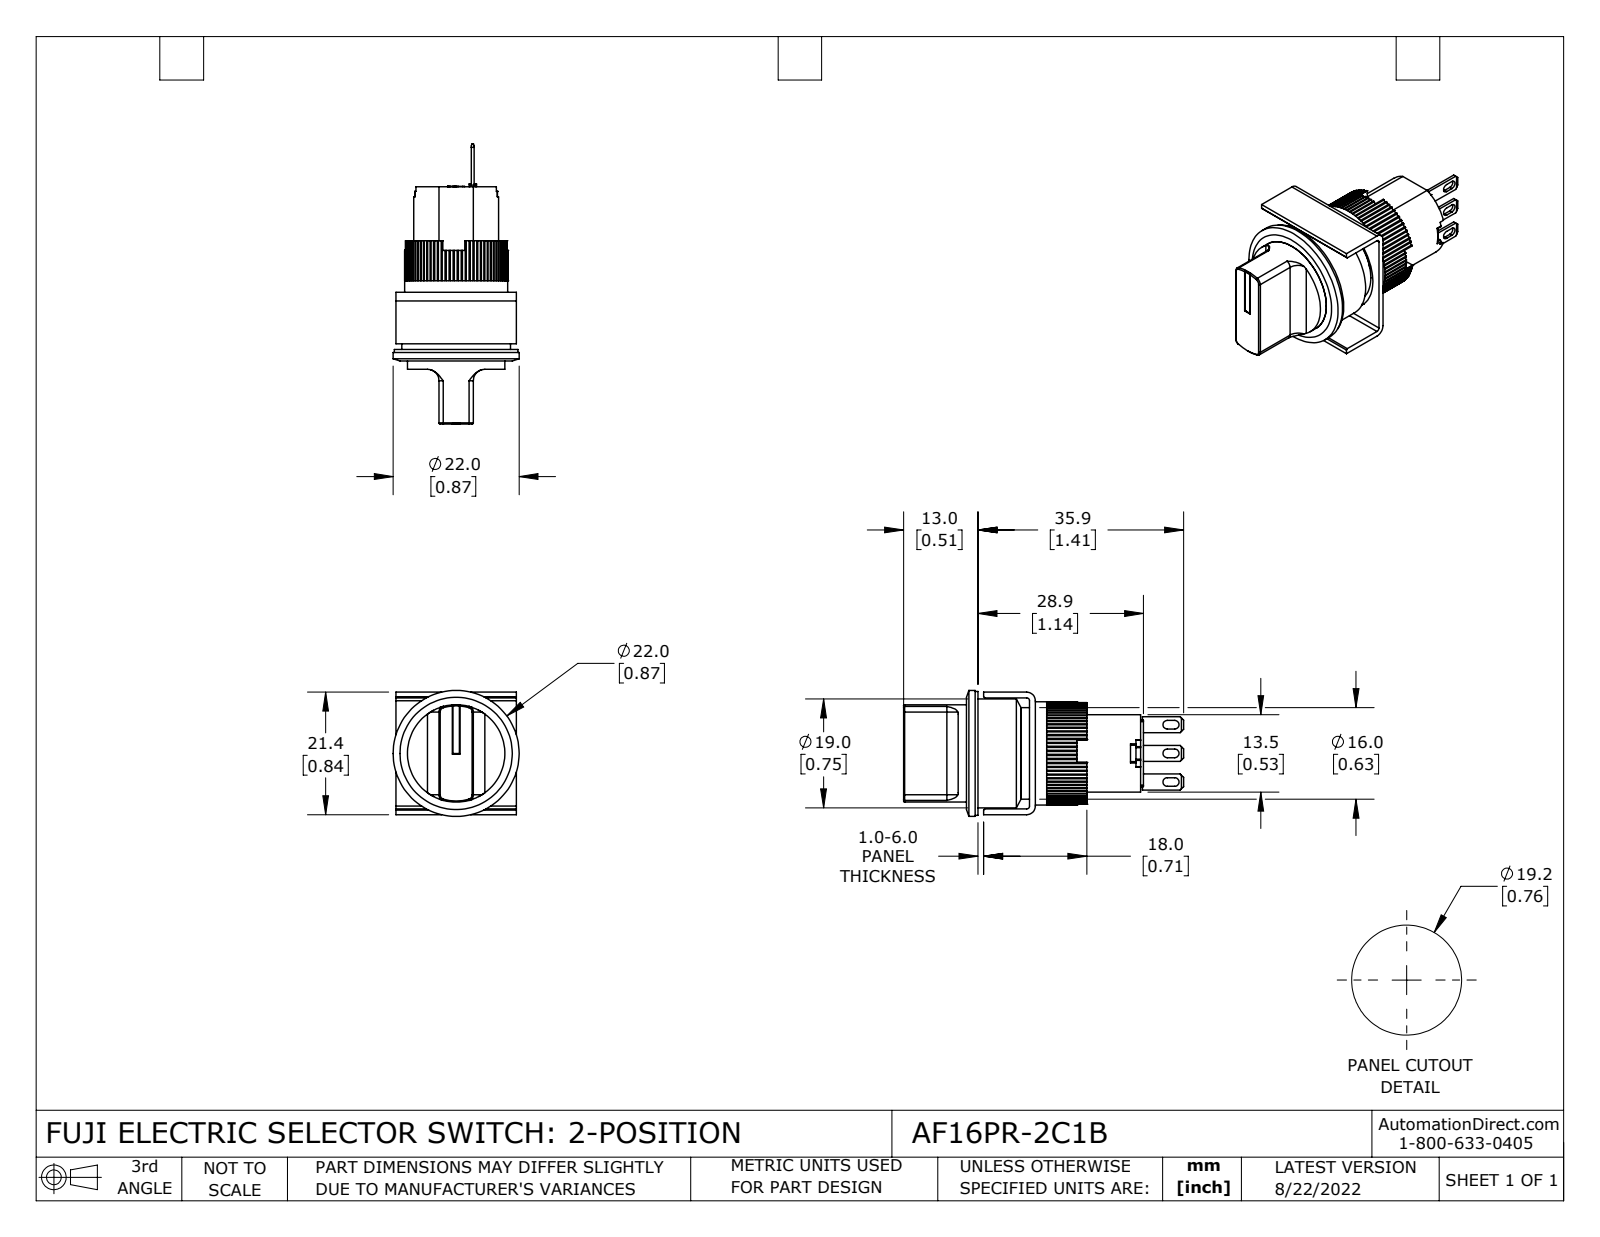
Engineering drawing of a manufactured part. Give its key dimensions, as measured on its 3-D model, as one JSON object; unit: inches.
{"part_name": "AF16PR-2C1B", "step_written_by": "SolidWorks 2021 (CONFIG_CONTROL_DESIGN)", "units": "inches", "bodies": {"solids": 9, "faces": 638, "planar": 443, "cylindrical": 180, "other": 15}, "overall_size": [1.925, 0.866, 0.866], "volume_in3": 0.491, "surface_area_in2": 10.18, "round_holes": [[0.039, 1], [0.669, 1], [0.709, 1], [0.748, 1]], "round_bosses_or_shafts": [[0.866, 1], [0.85, 1], [0.63, 1], [0.583, 1]], "partial_cylinders_radius": [[0.01, 80], [0.008, 14], [0.03, 6], [0.039, 4], [0.02, 2], [0.059, 2], [0.079, 2], [0.331, 1]], "face_to_face_distances": [0.374, 0.039, 0.059, 0.803, 0.764, 0.433, 0.232, 0.142, 0.116, 0.155]}
